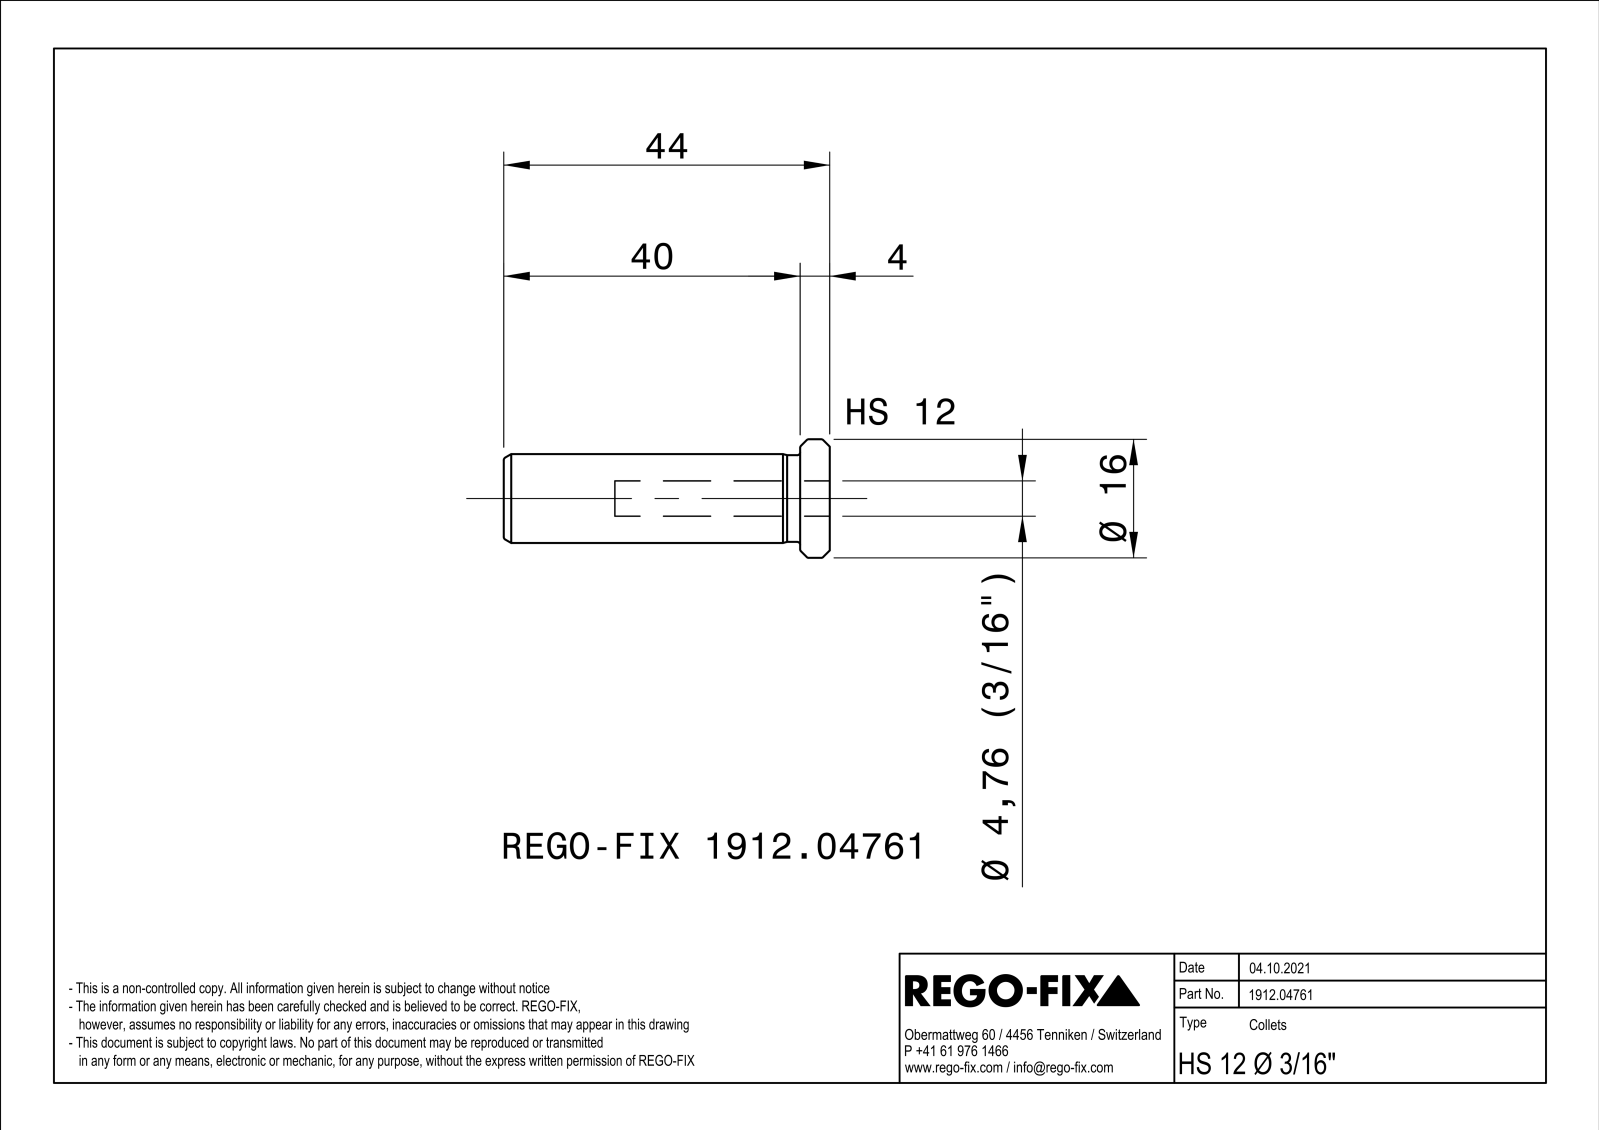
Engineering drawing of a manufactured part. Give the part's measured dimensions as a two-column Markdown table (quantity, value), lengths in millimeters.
| quantity | value |
| --- | --- |
| part name | NOCUT |
| STEP written by | SIEMENS PLM Software Solid Edge ST10 (AUTOMOTIVE_DESIGN) |
| units | millimeters |
| bodies | 1 solid, 70 faces (14 planar, 11 cylindrical, 45 other) |
| overall size | 44 × 15.98 × 15.98 |
| volume | 3 756 mm³ |
| surface area | 3 495 mm² |
| round holes (diameter × count) | 4.76 × 1, 7.5 × 1 |
| round bosses / shafts (diameter × count) | 16 × 1, 12 × 1, 11.7 × 1 |
| main face-to-face distances | 0.8, 44, 4, 40 |
